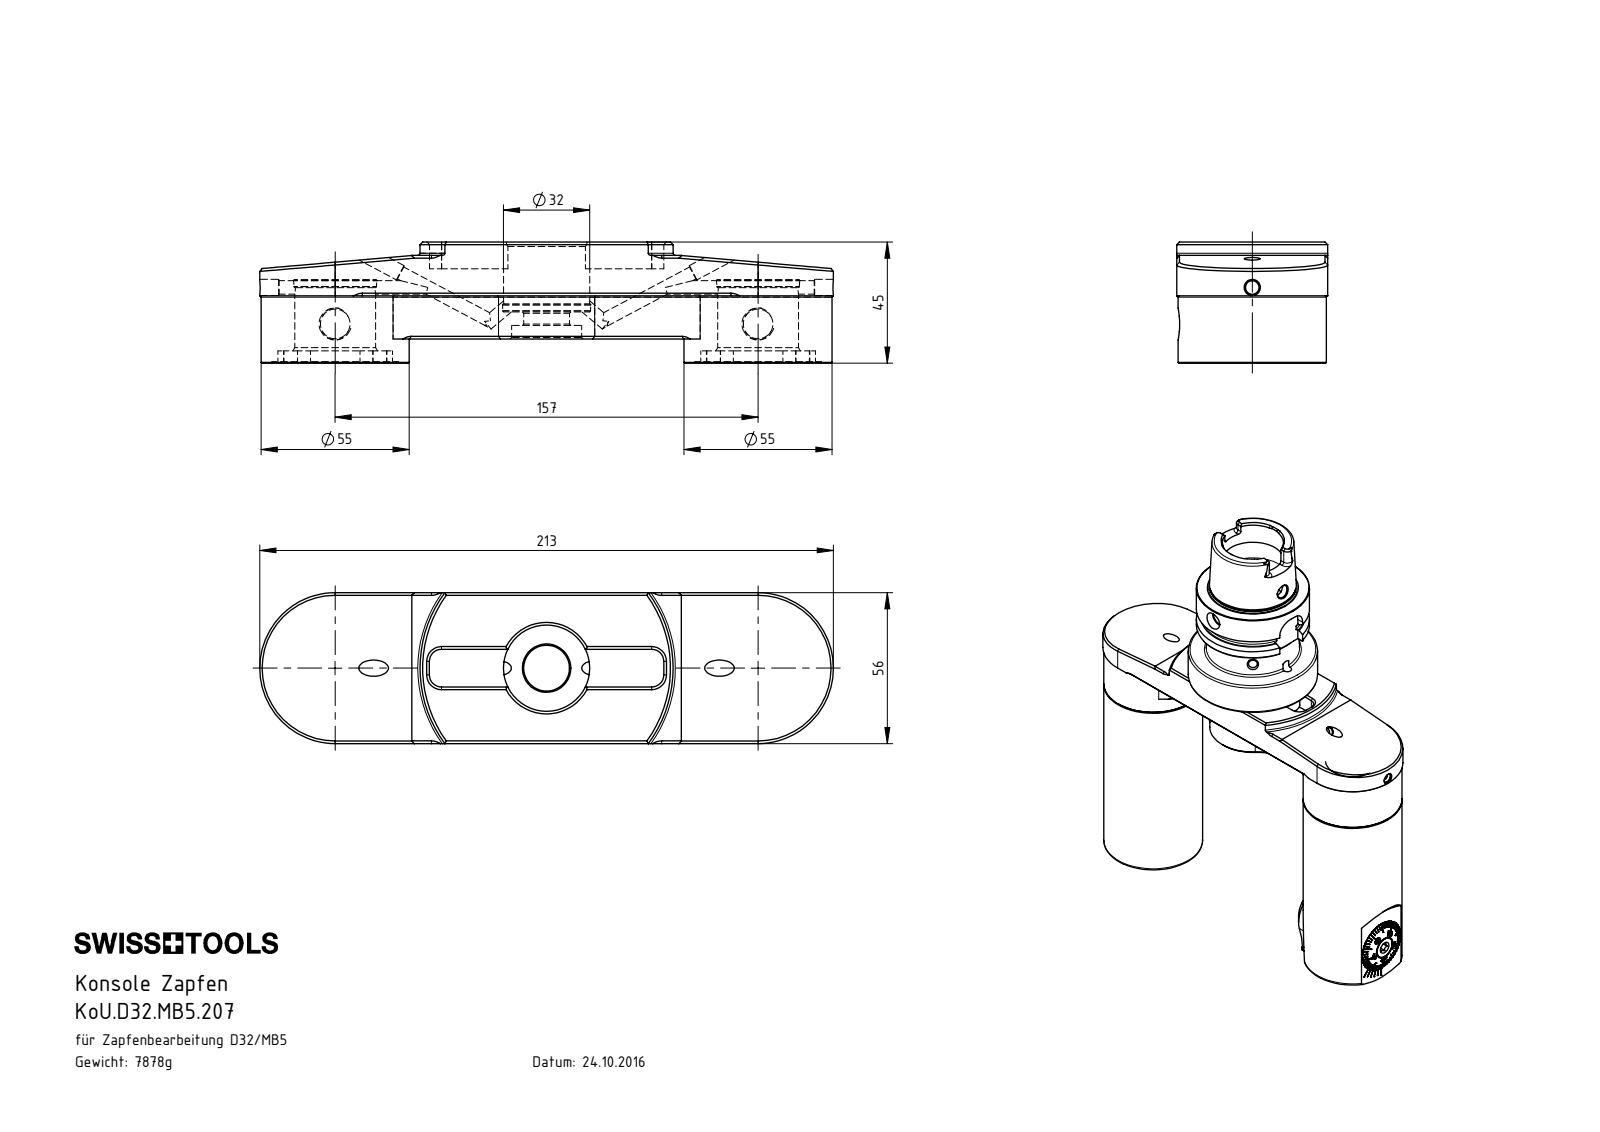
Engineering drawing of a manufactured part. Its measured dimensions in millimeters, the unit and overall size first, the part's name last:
Units: millimetres
Overall size (bounding box): 213 × 160 × 56
Round holes (diameter × count): ⌀5 ×7, ⌀6 ×4, ⌀11 ×2, ⌀30 ×2, ⌀31 ×2, ⌀47 ×2, ⌀2 ×1, ⌀8 ×1, ⌀14 ×1, ⌀17 ×1, ⌀26 ×1, ⌀32 ×1
Round bosses / shafts (diameter × count): ⌀6 ×3, ⌀55 ×2, ⌀12 ×2, ⌀24 ×1, ⌀16 ×1
Partial cylindrical surfaces — rounded edges, fillets, slot ends (radius × count): R5.2 ×8, R4.5 ×4, R25.64 ×4, R18.5 ×2, R21.27 ×2, R28 ×2, R21.02 ×1, R24 ×1
Main face-to-face distances: 5, 20, 16, 9, 14, 10, 31, 21, 56, 6
Hole centre spacings: 157, 78.5, 0.35
Volume: 537 268 mm³ · Surface area: 91 871 mm²
Bodies: 13 solids, 515 faces (119 planar, 134 cylindrical, 262 other)
Part name (STEP PRODUCT): CWF-MB5.Ko1.105_A; DIN 7984 - M16 x 35; KoU-D32.MB5.207_D_KoU-D32.WN4.147; 222.550.207 (+2 more)
STEP written by: SolidWorks 2017 (CONFIG_CONTROL_DESIGN)
